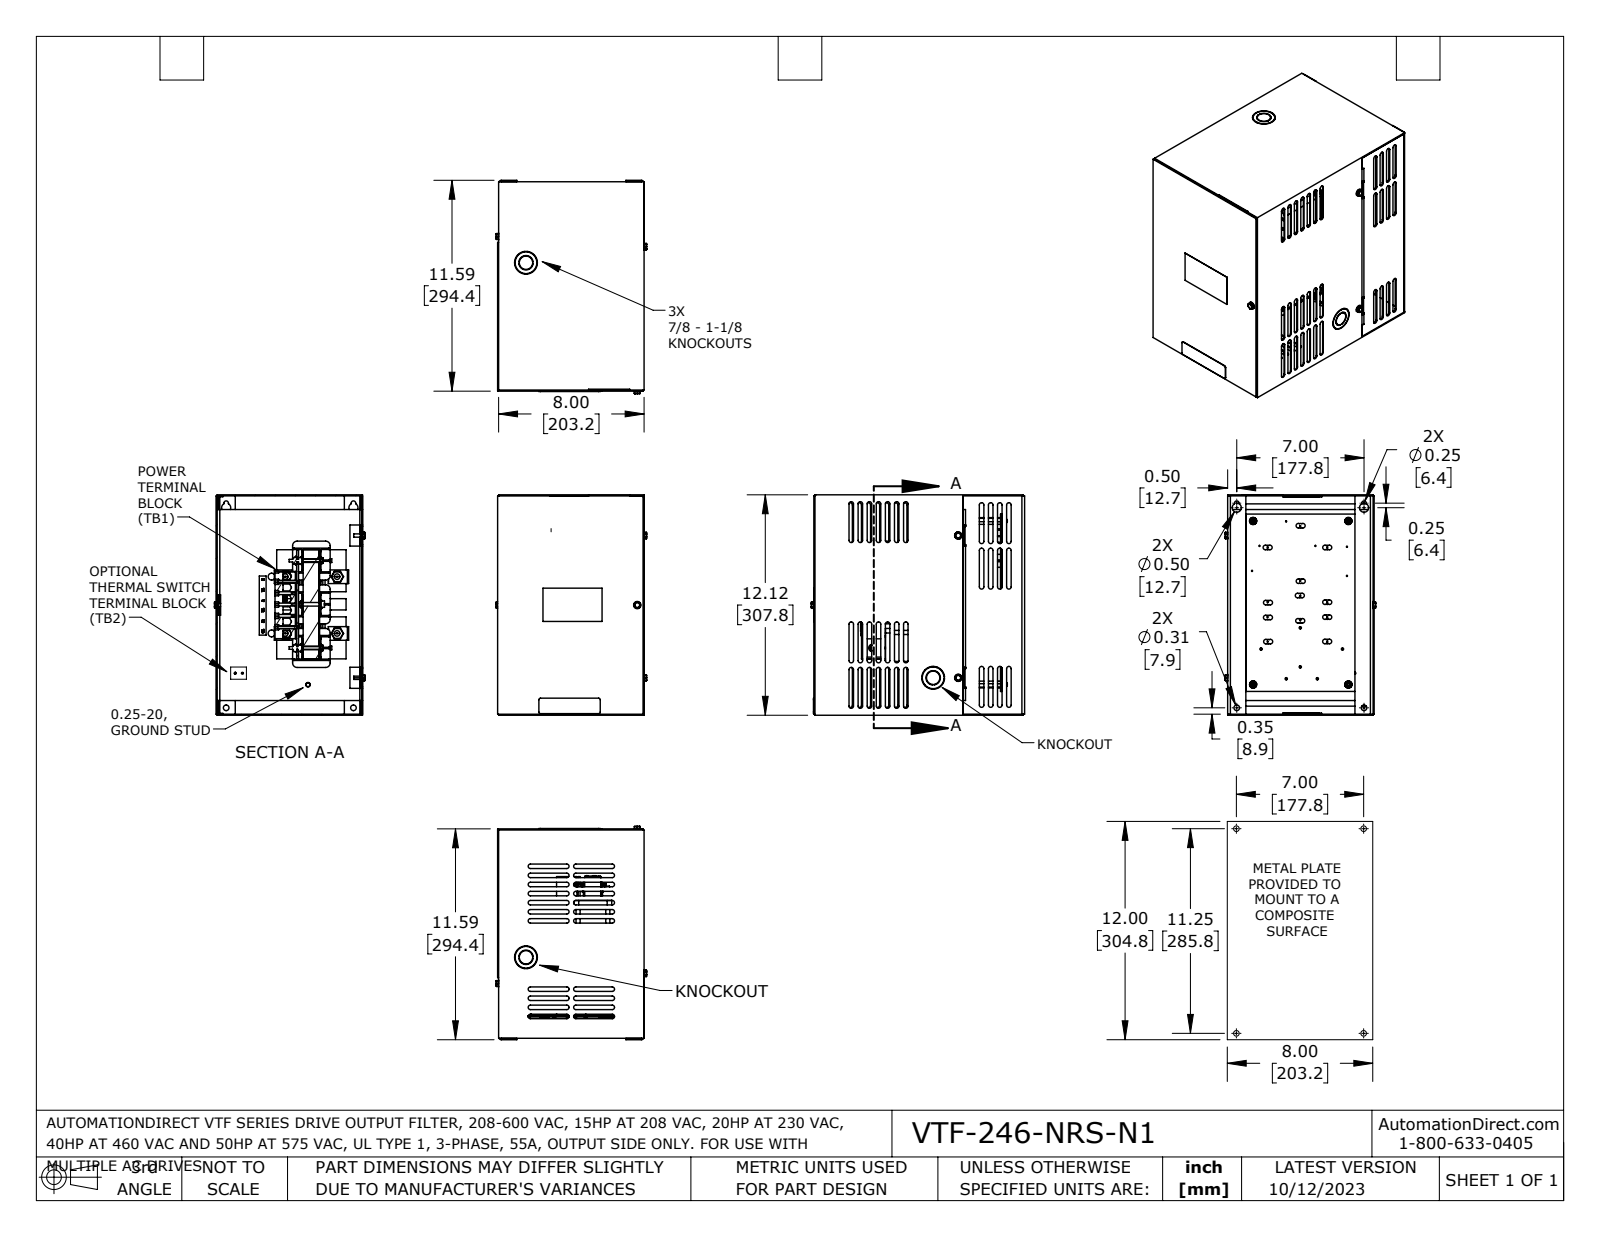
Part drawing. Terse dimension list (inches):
name: VTF-246-NRS-N1
written by: SolidWorks 2021 (AUTOMOTIVE_DESIGN)
unit: in
bodies: 49 solids, 4013 faces (2037 planar, 1469 cylindrical, 507 other)
size: 12.12 × 11.736 × 8.287
volume: 106.6 in³; area: 1 951 in²
holes: 24× ⌀0.06, 16× ⌀0.276, 11× ⌀0.25, 9× ⌀0.31, 6× ⌀0.164, 6× ⌀0.22, 6× ⌀0.38, 5× ⌀0.186, 3× ⌀0.1, 3× ⌀0.125, 3× ⌀0.202, 2× ⌀0.104
bosses: 5× ⌀0.5, 5× ⌀0.164, 5× ⌀0.125, 4× ⌀0.608, 4× ⌀0.414, 4× ⌀0.306, 4× ⌀0.21, 4× ⌀0.181
rounds: 140× R0.123, 87× R0.125, 44× R0.025, 44× R0.25, 42× R0.01, 24× R0.03, 24× R0.038, 20× R0.05
face distances: 0.075, 0.059, 12.059, 10.277, 8.193, 2.085, 0.047, 8.008, 8.055, 0.062
hole spacings: 0.465, 0.398, 0.635, 0.787, 0.821, 1.25, 1.257, 1.34
